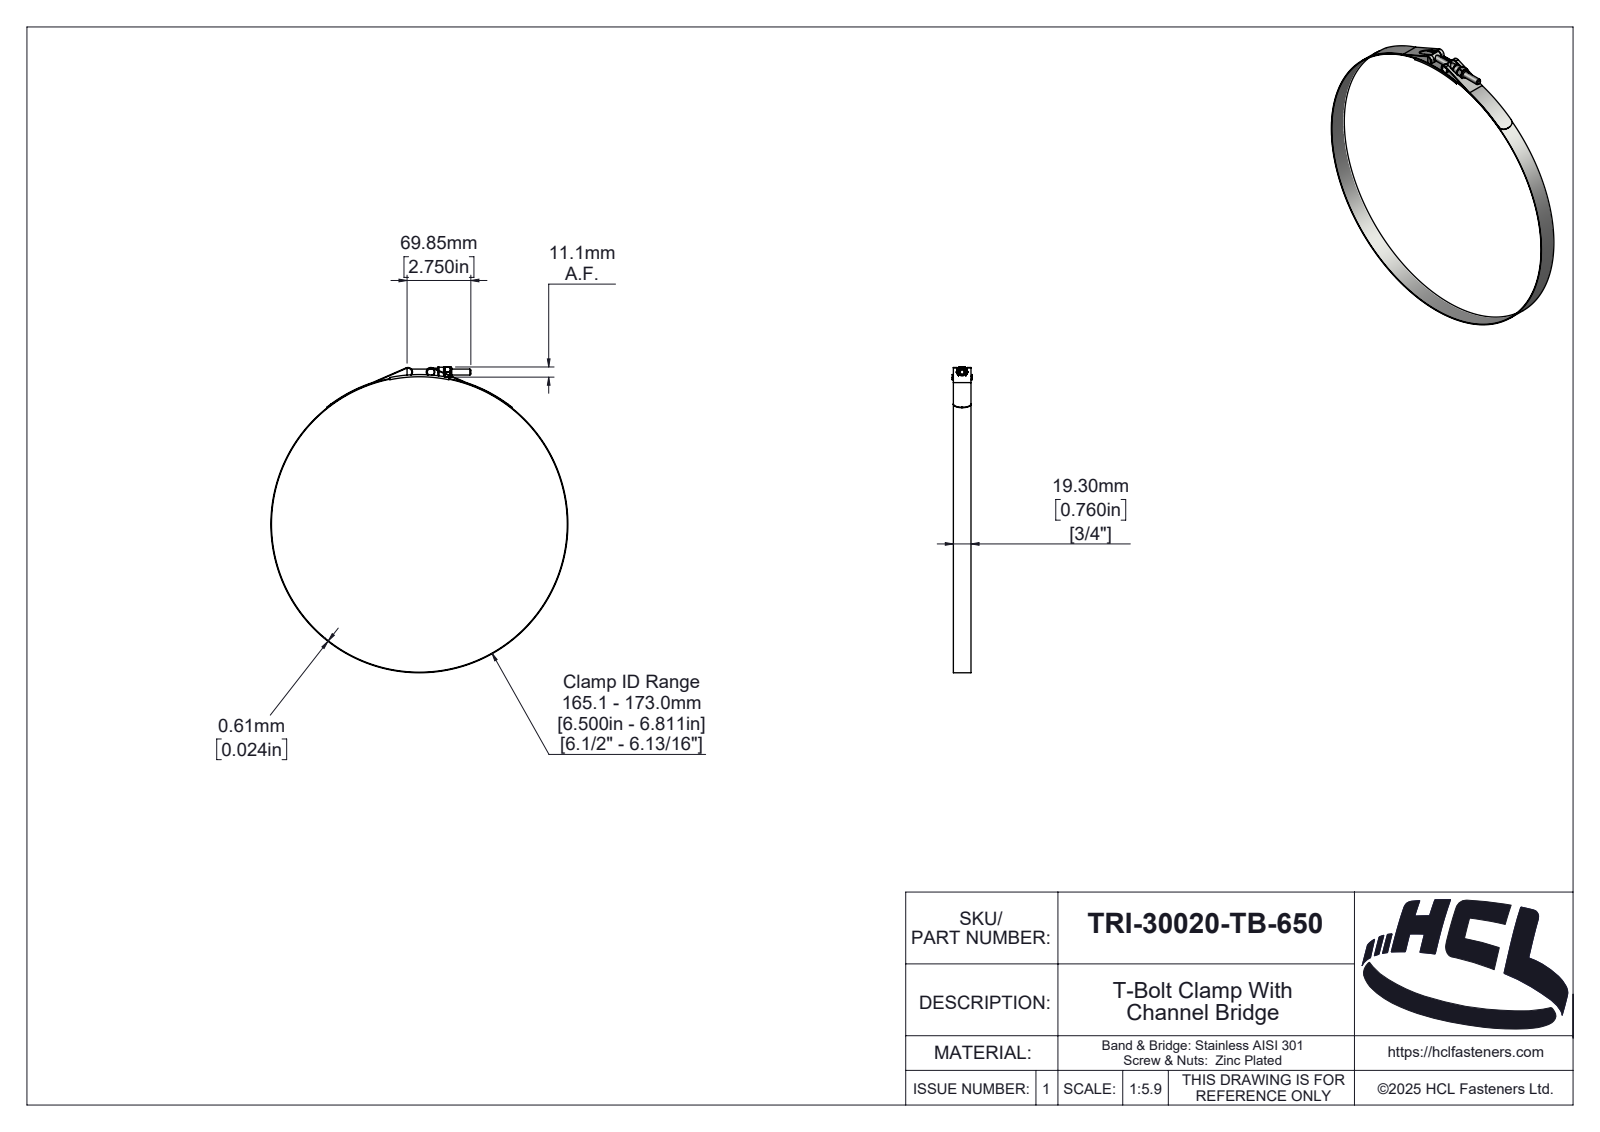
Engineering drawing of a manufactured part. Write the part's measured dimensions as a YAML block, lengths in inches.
part_name: "TRI-30020-TB-650"
step_written_by: "SolidWorks 2025 (AUTOMOTIVE_DESIGN)"
units: inches
bodies: {solids: 6, faces: 330, planar: 44, cylindrical: 122, other: 164}
overall_size: [13.183, 12.804, 0.866]
volume: 1.167
surface_area: 85.3
round_holes:
  - {diameter: 0.213, count: 1}
  - {diameter: 0.25, count: 1}
  - {diameter: 0.256, count: 1}
  - {diameter: 0.298, count: 1}
  - {diameter: 12.756, count: 1}
round_bosses_or_shafts:
  - {diameter: 0.338, count: 2}
  - {diameter: 12.804, count: 1}
  - {diameter: 0.417, count: 1}
partial_cylinders:
  - {radius: 0.015, count: 6}
  - {radius: 0.02, count: 2}
  - {radius: 0.173, count: 2}
  - {radius: 0.197, count: 2}
  - {radius: 0.023, count: 1}
  - {radius: 0.095, count: 1}
  - {radius: 0.119, count: 1}
  - {radius: 0.126, count: 1}
face_to_face_distances: [0.024, 0.76, 0.053, 0.813, 0.029, 0.842, 0.789, 0.866, 0.818, 0.437]
hole_center_spacings: [6.575]
